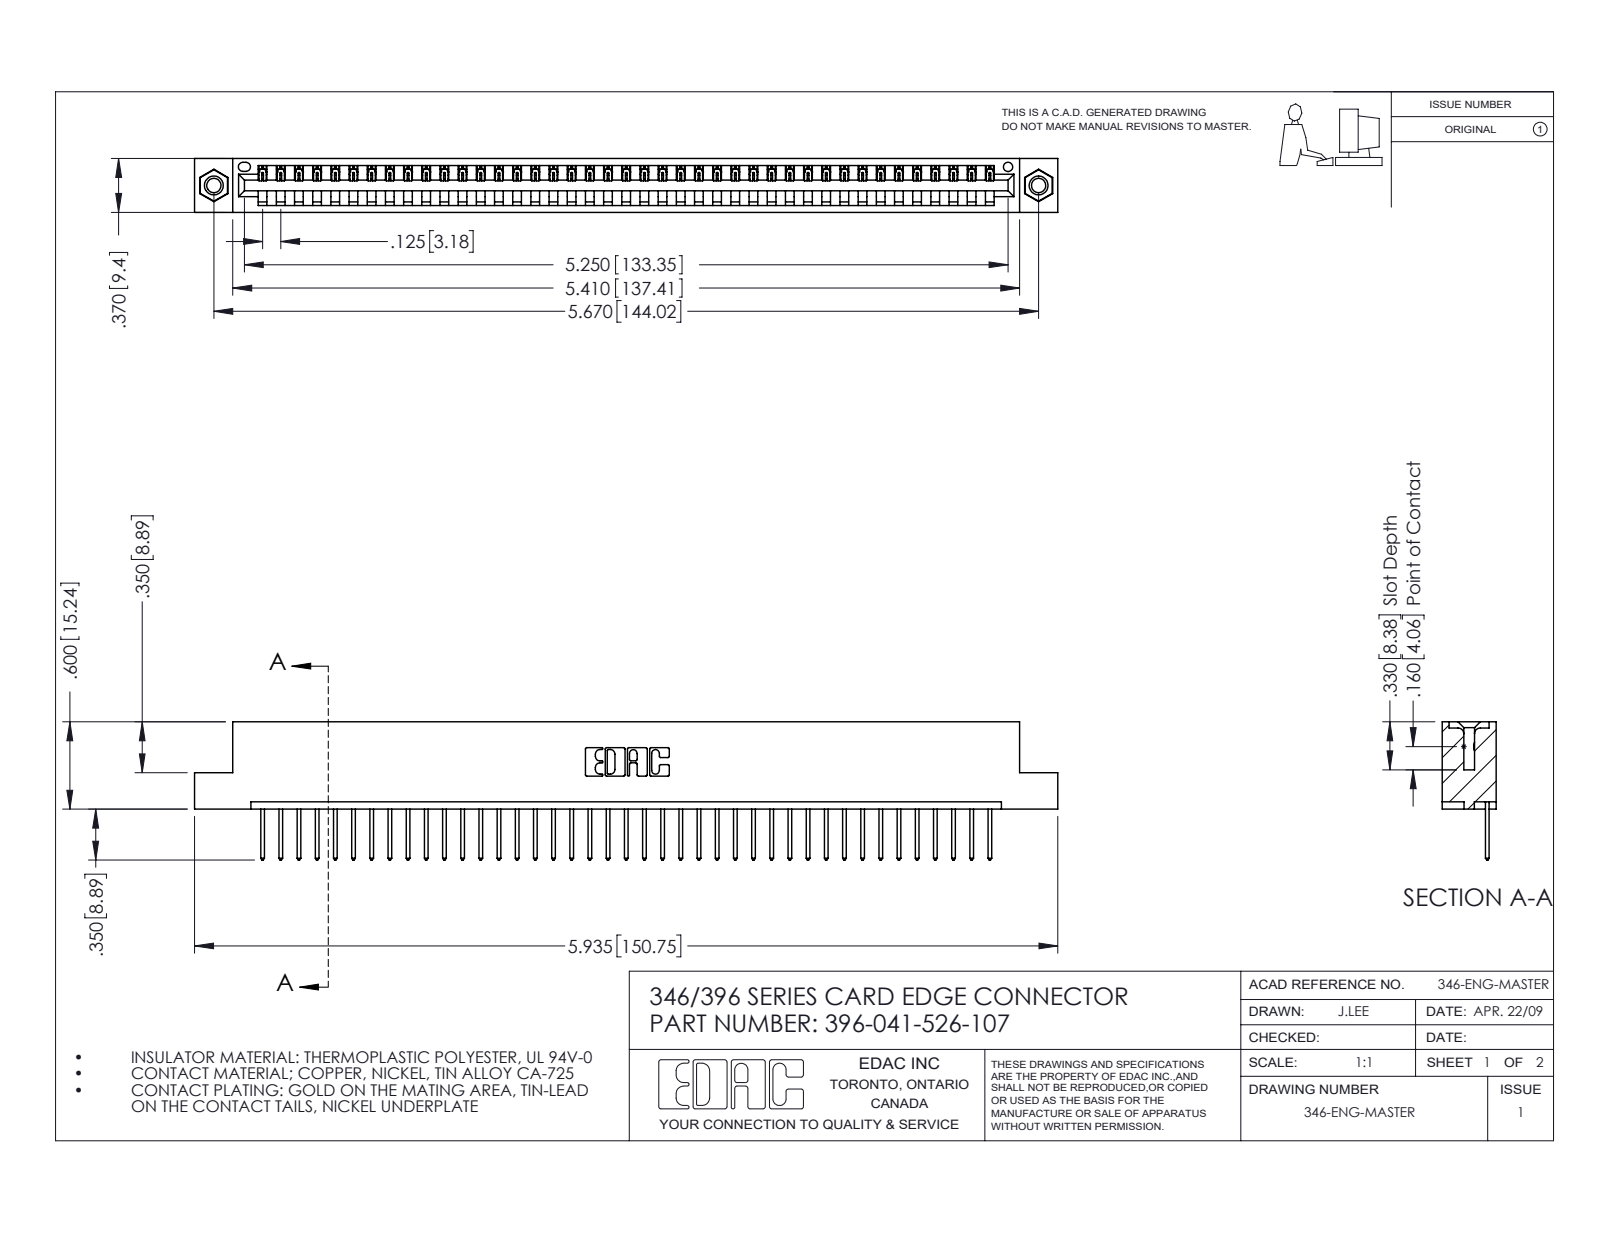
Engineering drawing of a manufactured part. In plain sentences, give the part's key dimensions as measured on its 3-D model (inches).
The part is named "396-041-526-107; 345-250-001_345-250-005-103; 345-292-001_345-293-126; 346 Part_Flush Mounting Lugs - 0.156 Dia-TI". Its 3-D file was written by "SolidWorks 2016 (CONFIG_CONTROL_DESIGN)". It is 44 solids with 2560 faces: 1748 planar, 796 cylindrical and 16 other. Overall it measures 5.935 by 0.95 by 0.37 inches. Its volume is 0.877 cubic inches and its surface area 27.83 square inches. Round holes: 2 of diameter 0.098, 2 of diameter 0.125, 2 of diameter 0.156, 1 of diameter 0.064. Round bosses or shafts: 2 of diameter 0.155. Partial cylindrical surfaces (rounded edges, fillets, slot ends): 82 of radius 0.006, 82 of radius 0.01, 22 of radius 0.01, 6 of radius 0.007, 6 of radius 0.031, 3 of radius 0.026, 2 of radius 0.031, 2 of radius 0.04. The main face-to-face distances are 0.048, 0.322, 0.37, 0.25, 0.072, 0.298, 0.025, 0.148, 0.222, 0.1. The hole center spacings are 0.246, 5.461, 5.67.
